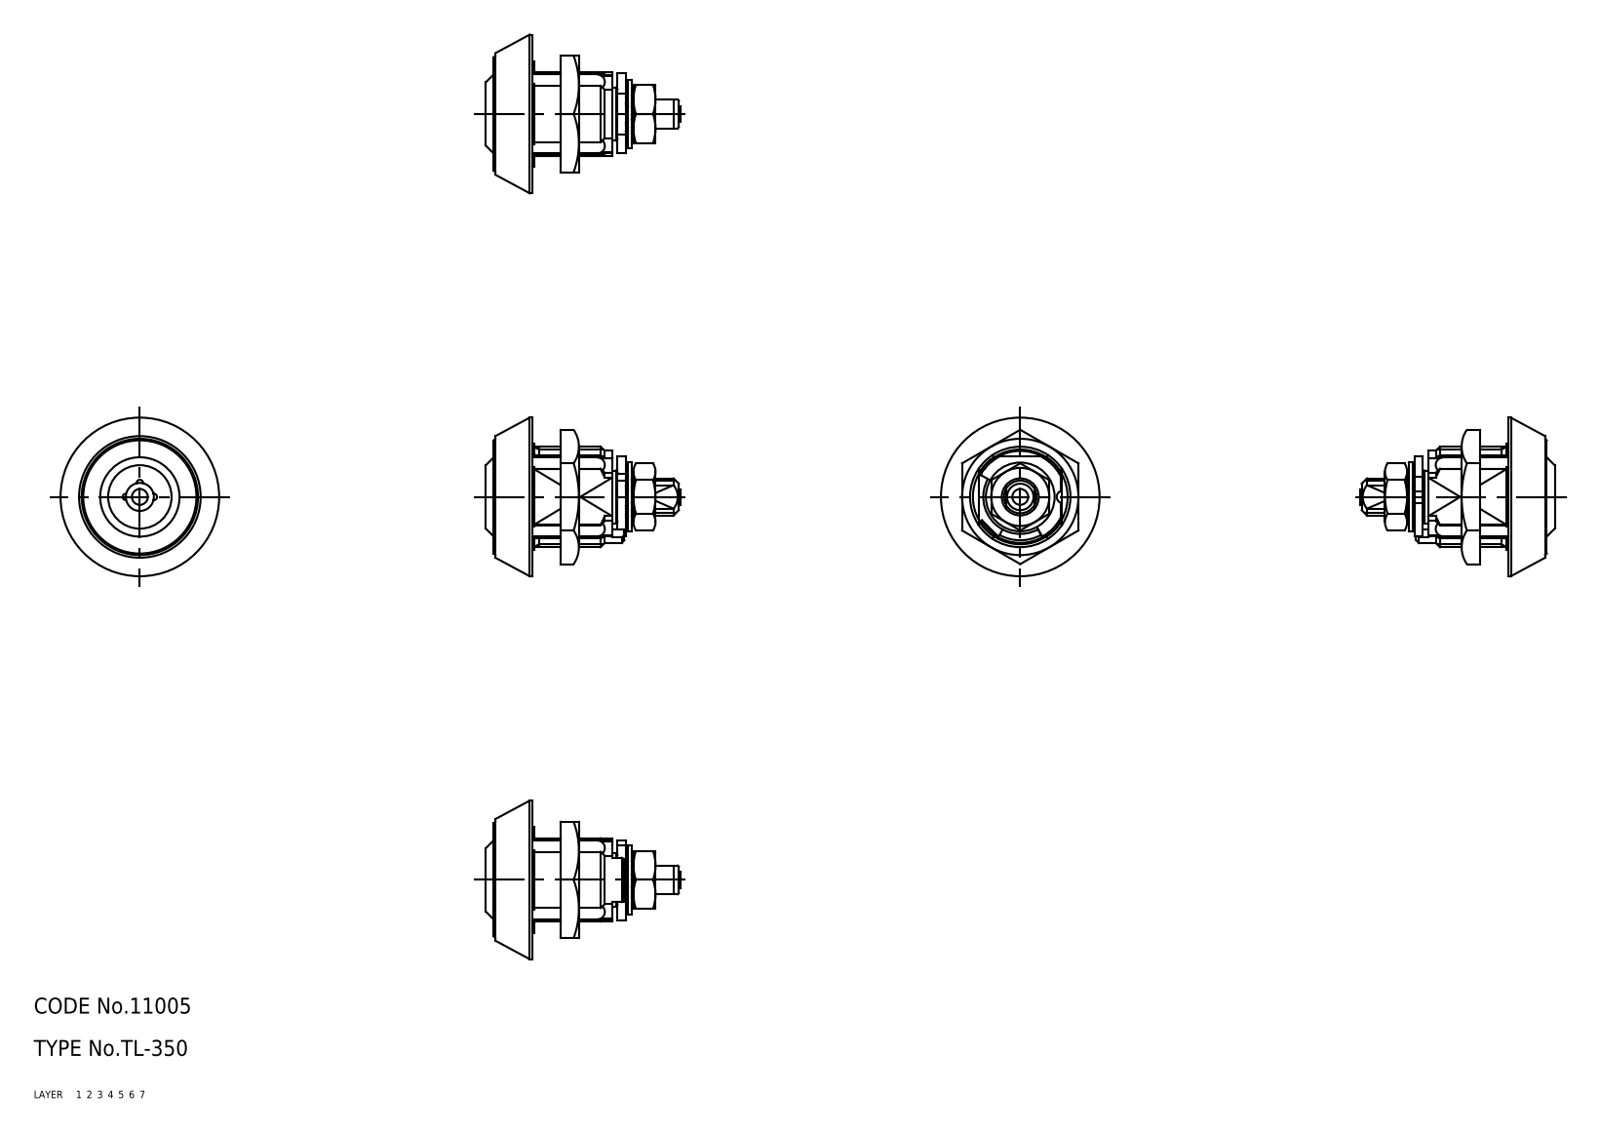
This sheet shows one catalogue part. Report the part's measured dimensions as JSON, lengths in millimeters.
{"part_name": "washer; ring; nut_B; nut_A (+3 more)", "step_written_by": "CADfix (AUTOMOTIVE_DESIGN)", "units": "millimeters", "bodies": {"solids": 6, "faces": 170, "planar": 0, "cylindrical": 0, "other": 170}, "overall_size": [36.8, 30, 30], "volume_mm3": 9392, "surface_area_mm2": 6107}
